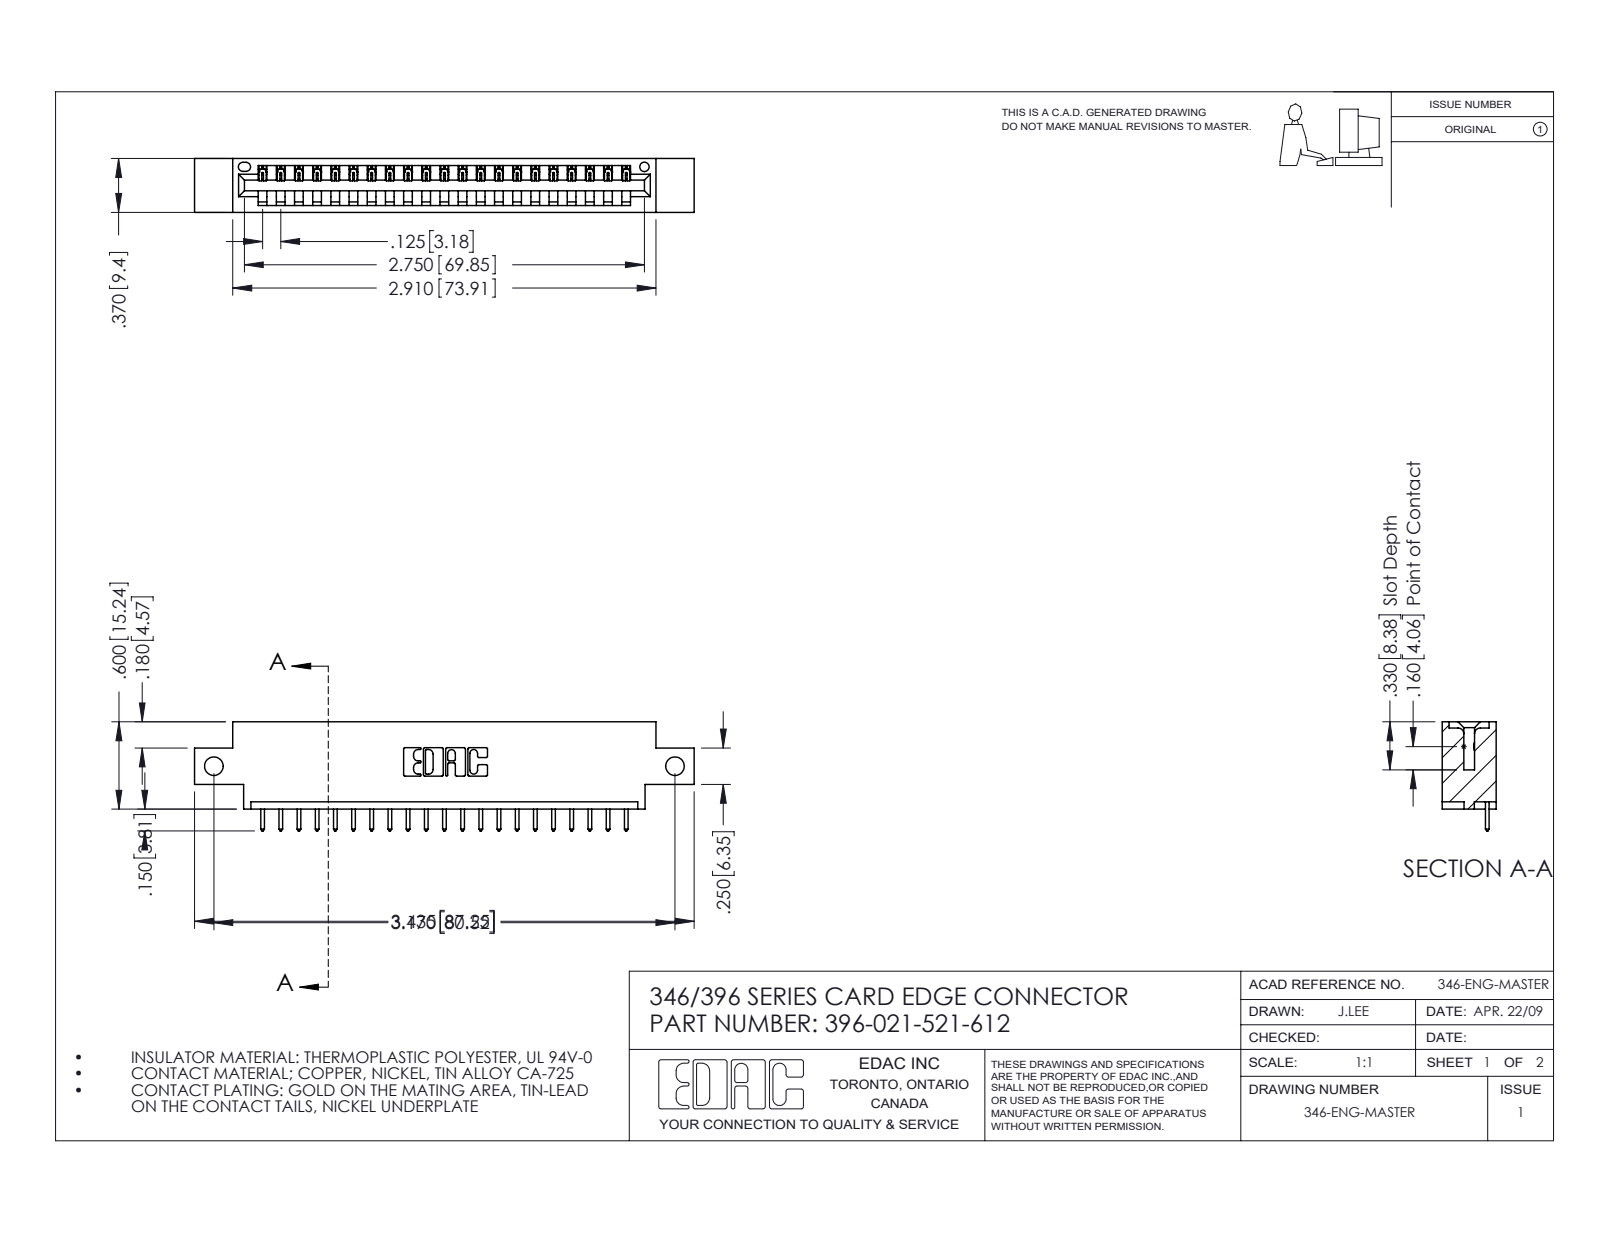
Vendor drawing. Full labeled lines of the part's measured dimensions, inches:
Part name (STEP PRODUCT): 396-021-521-612; 345-292-001_345-293-121; 346 Part_0.170 Offset - Side Mount
STEP written by: SolidWorks 2016 (CONFIG_CONTROL_DESIGN)
Units: inches
Bodies: 22 solids, 1344 faces (920 planar, 424 cylindrical, 0 other)
Overall size (bounding box): 3.435 × 0.75 × 0.37
Volume: 0.482 in³ · Surface area: 14.62 in²
Round holes (diameter × count): ⌀0.128 ×2, ⌀0.064 ×1
Partial cylindrical surfaces — rounded edges, fillets, slot ends (radius × count): R0.006 ×42, R0.01 ×42, R0.01 ×22, R0.007 ×6, R0.031 ×6, R0.026 ×3, R0.031 ×2, R0.04 ×2
Main face-to-face distances: 0.048, 0.322, 0.37, 0.25, 0.072, 0.298, 0.025, 0.148, 0.222, 0.1
Hole centre spacings: 3.17
